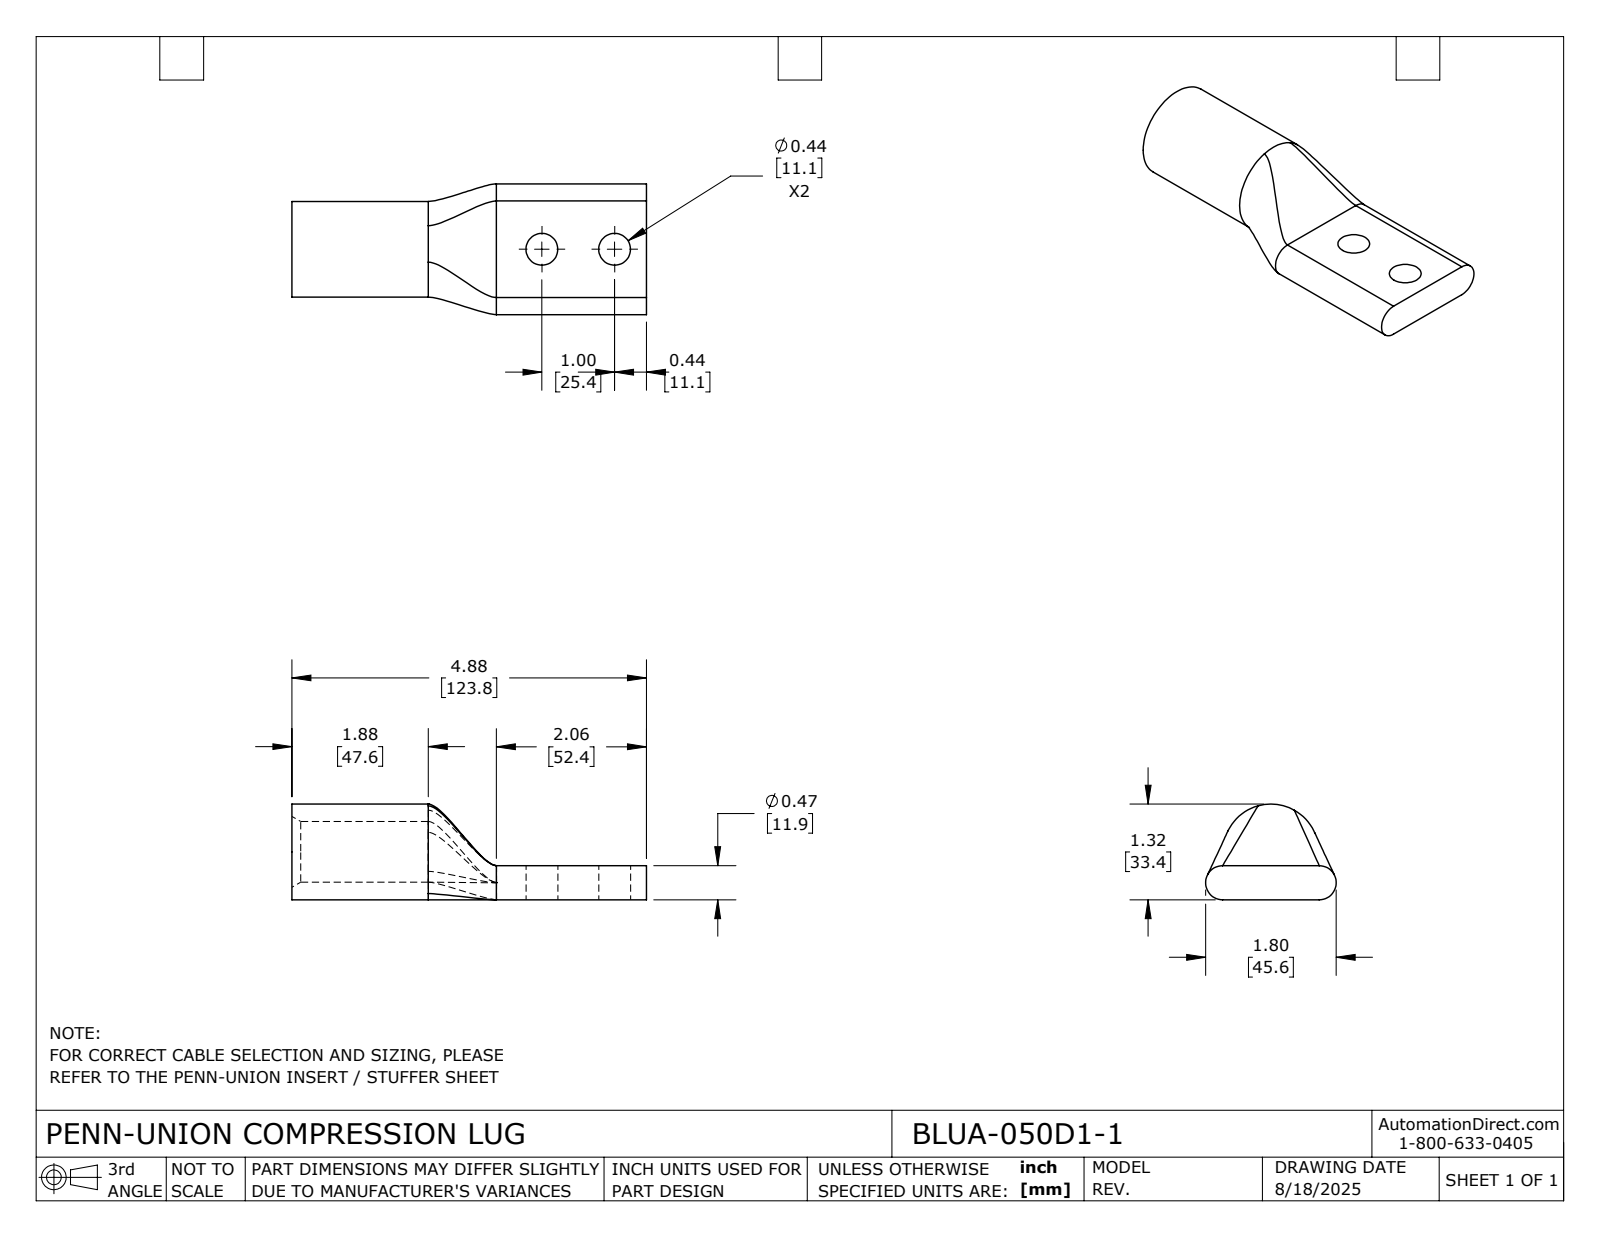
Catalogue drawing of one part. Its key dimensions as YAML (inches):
part_name: "BLUA-050D1-1"
step_written_by: "SolidWorks 2024 (CONFIG_CONTROL_DESIGN)"
units: inches
bodies: {solids: 1, faces: 26, planar: 5, cylindrical: 11, other: 10}
overall_size: [4.875, 1.797, 1.315]
volume: 3.758
surface_area: 30.37
round_holes:
  - {diameter: 0.437, count: 2}
  - {diameter: 0.834, count: 1}
round_bosses_or_shafts:
  - {diameter: 1.315, count: 1}
partial_cylinders:
  - {radius: 0.234, count: 2}
face_to_face_distances: [0.469, 4.875, 2.813, 2.062]
hole_center_spacings: [1]
